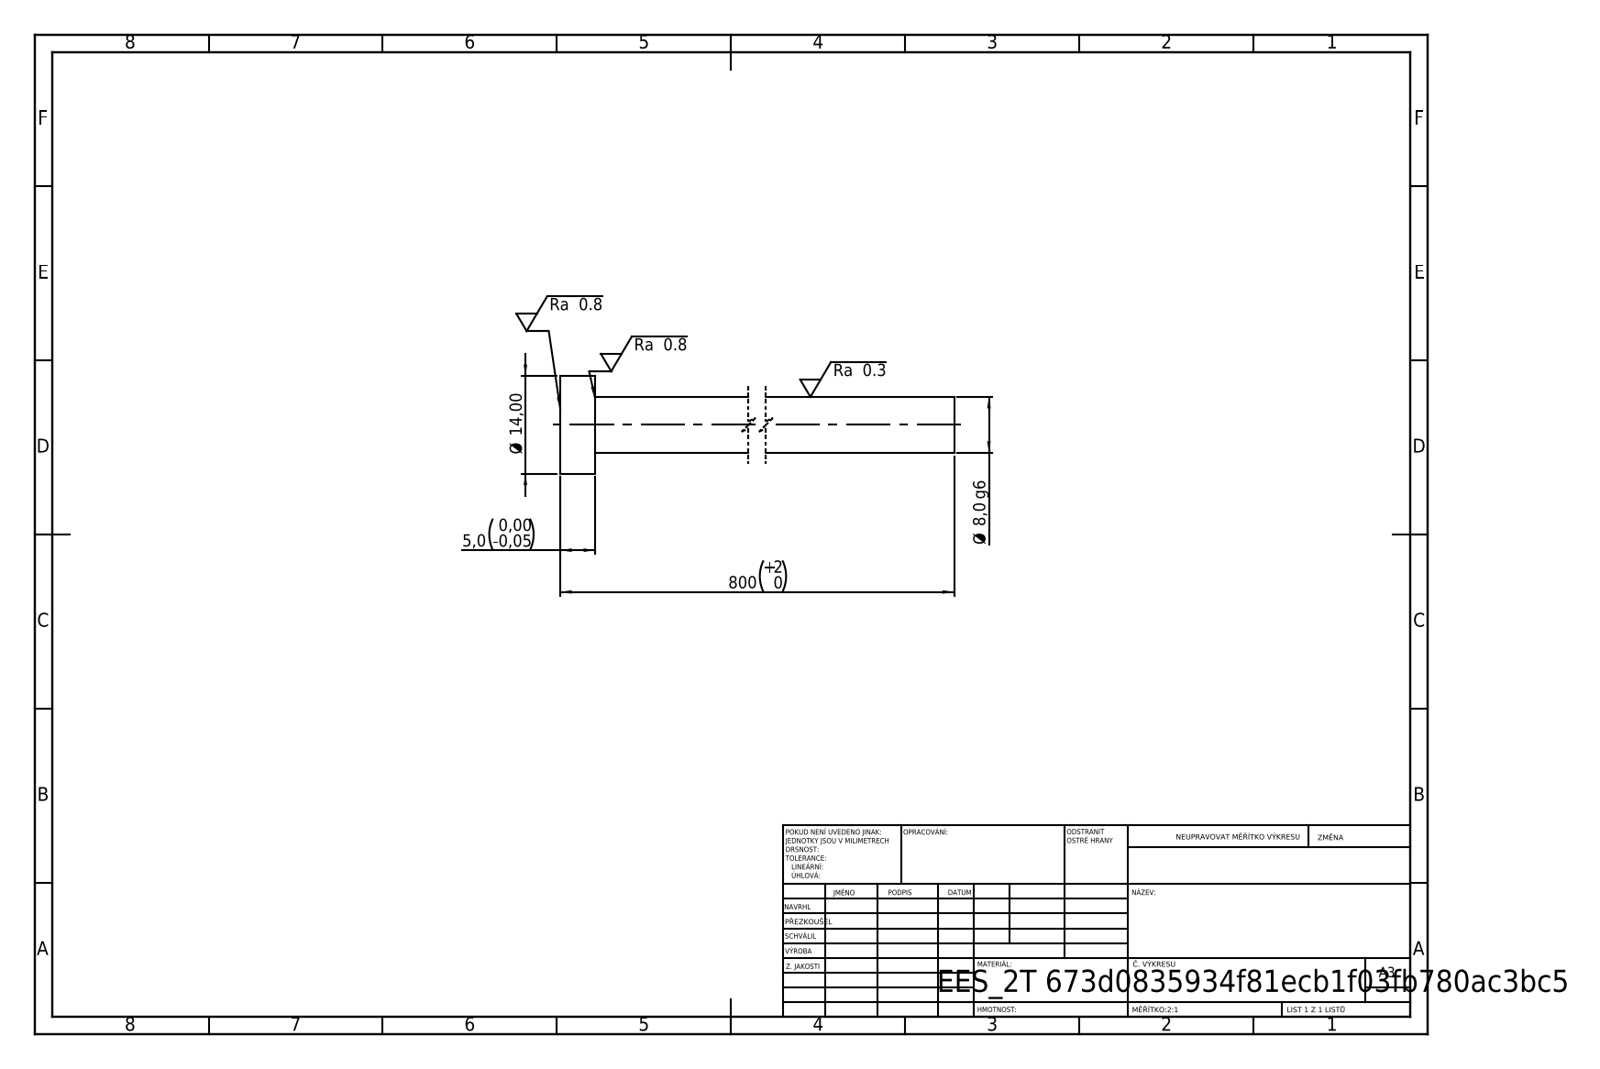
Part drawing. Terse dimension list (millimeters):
written by: SolidWorks 2019 (CONFIG_CONTROL_DESIGN)
unit: mm
bodies: 1 solid, 7 faces (3 planar, 4 cylindrical, 0 other)
size: 800 × 14 × 14
volume: 40 731 mm³; area: 20 508 mm²
bosses: 1× ⌀14, 1× ⌀8
face distances: 5, 800, 795
